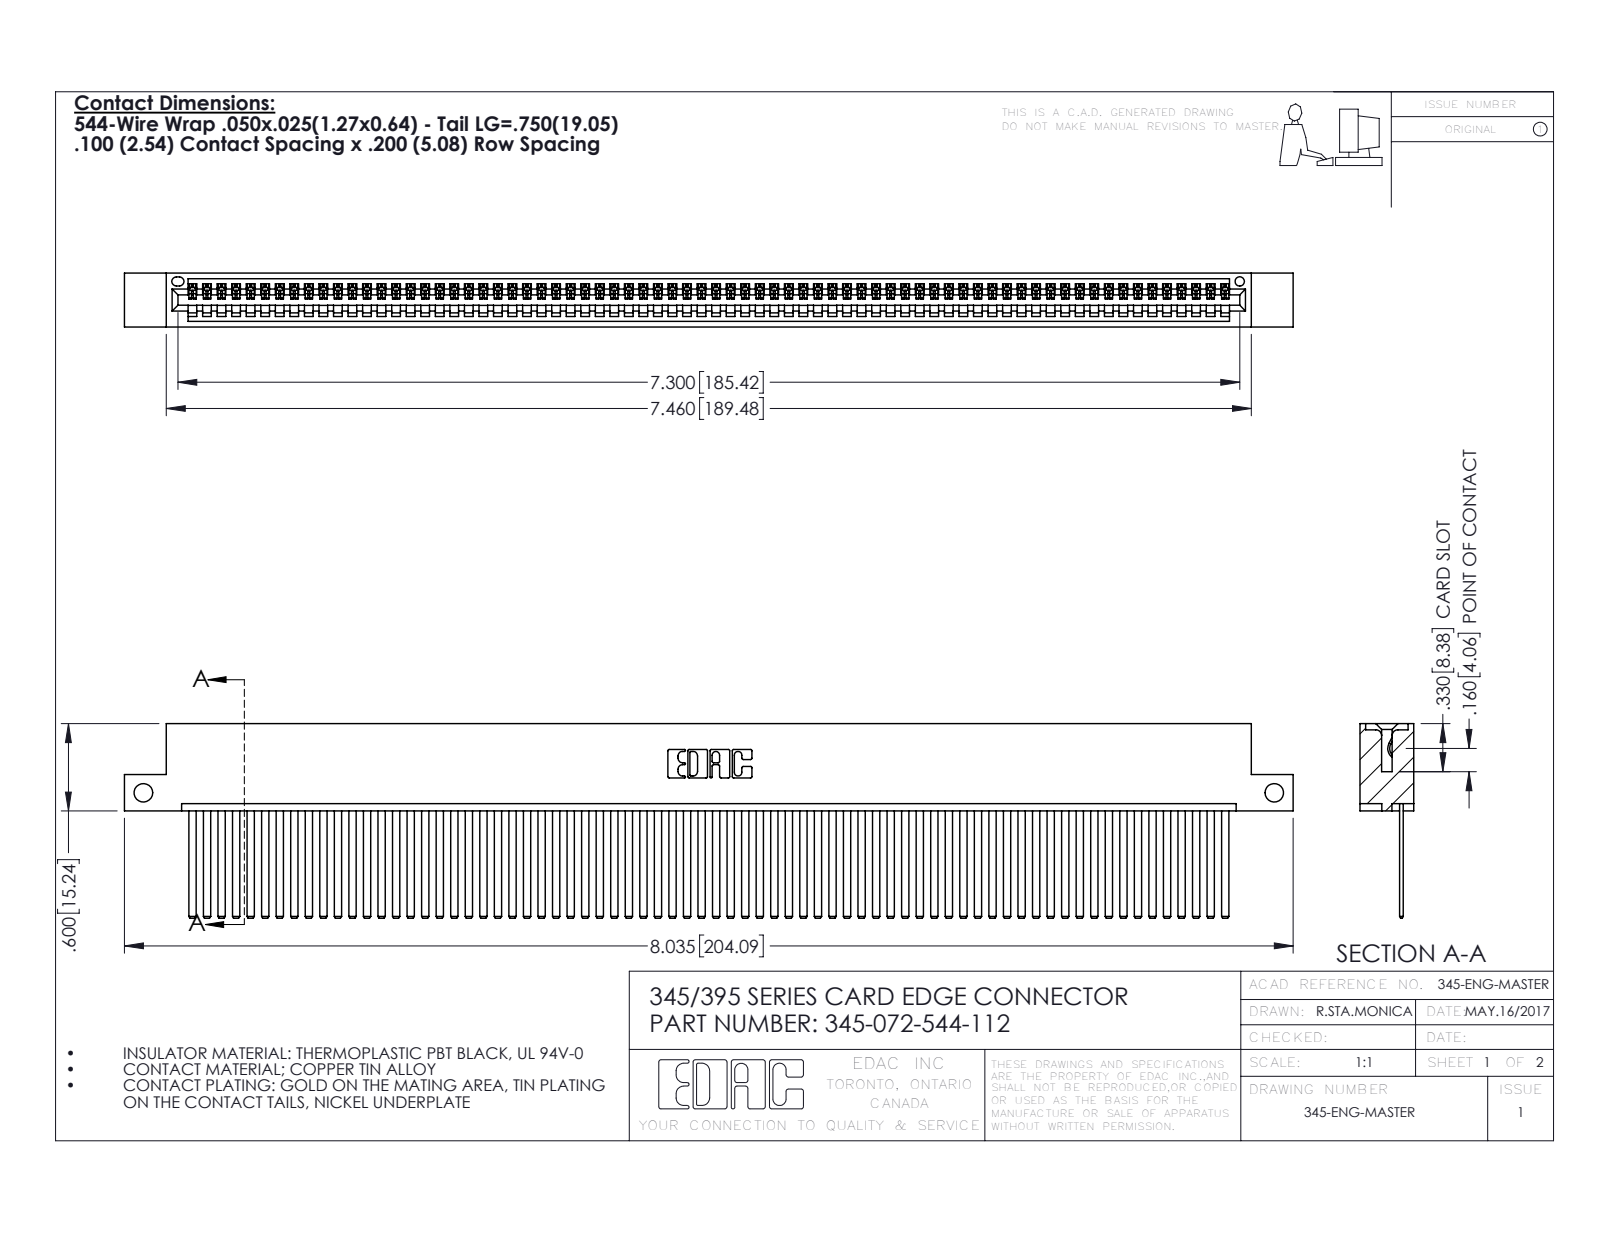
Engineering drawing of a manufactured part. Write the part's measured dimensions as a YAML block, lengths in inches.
part_name: "345-072-544-112; 345 Part_Flush Mounting Lugs - Side Mount; 345-292-001_345-293-144"
step_written_by: "SolidWorks 2016 (CONFIG_CONTROL_DESIGN)"
units: inches
bodies: {solids: 73, faces: 3870, planar: 2672, cylindrical: 1198, other: 0}
overall_size: [8.035, 1.337, 0.37]
volume: 1.243
surface_area: 46.26
round_holes:
  - {diameter: 0.128, count: 2}
  - {diameter: 0.064, count: 1}
partial_cylinders:
  - {radius: 0.006, count: 144}
  - {radius: 0.01, count: 22}
  - {radius: 0.007, count: 6}
  - {radius: 0.031, count: 6}
  - {radius: 0.026, count: 3}
  - {radius: 0.031, count: 2}
  - {radius: 0.04, count: 2}
  - {radius: 0.014, count: 1}
face_to_face_distances: [0.072, 0.298, 0.025, 0.098, 0.272, 0.37, 0.2, 0.225, 0.149, 0.072]
hole_center_spacings: [7.775]
